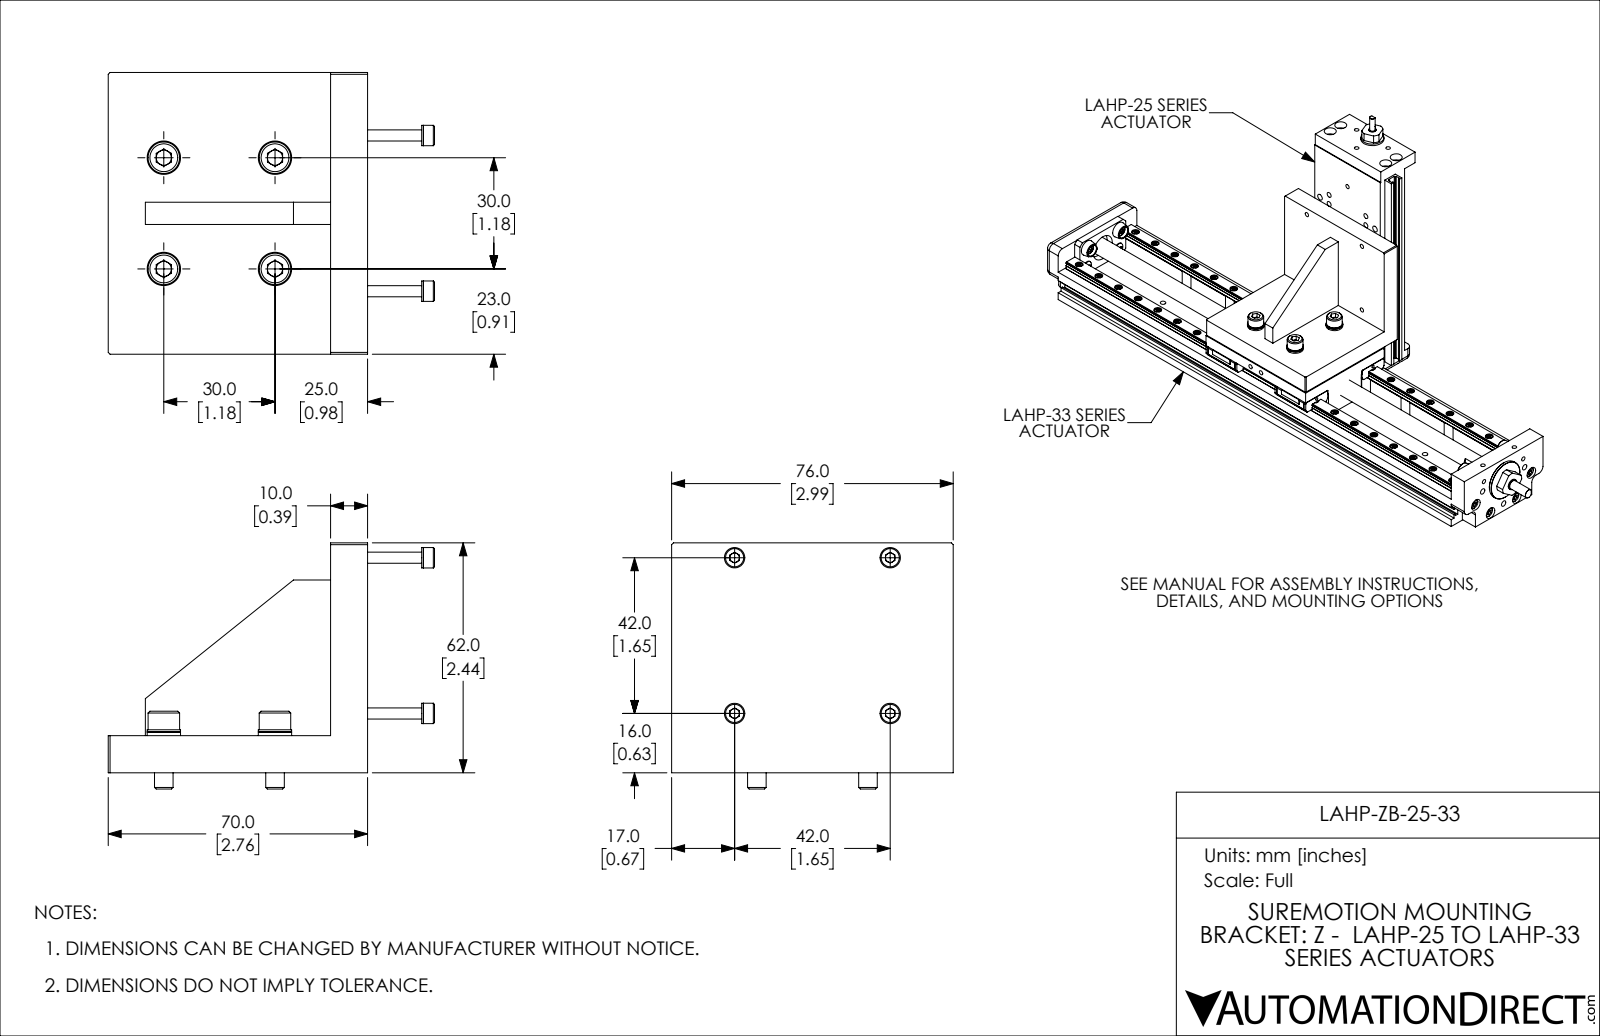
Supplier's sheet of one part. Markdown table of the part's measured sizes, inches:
| quantity | value |
| --- | --- |
| part name | LAHP-ZB-25-33 |
| STEP written by | SolidWorks 2019 (CONFIG_CONTROL_DESIGN) |
| units | inches |
| bodies | 21 solids, 321 faces (161 planar, 96 cylindrical, 64 other) |
| overall size | 3.467 × 2.992 × 2.614 |
| volume | 6.325 in³ |
| surface area | 47.21 in² |
| round holes (diameter × count) | 0.098 × 4, 0.126 × 4, 0.209 × 4, 0.217 × 4 |
| round bosses / shafts (diameter × count) | 0.354 × 4, 0.335 × 4, 0.217 × 4, 0.197 × 4, 0.118 × 4 |
| main face-to-face distances | 0.394, 1.614, 1.378, 0.236, 2.992, 2.362, 2.047, 2.756, 2.441, 0.433 |
| hole center spacings | 1.181, 1.654, 1.67, 2.339 |
